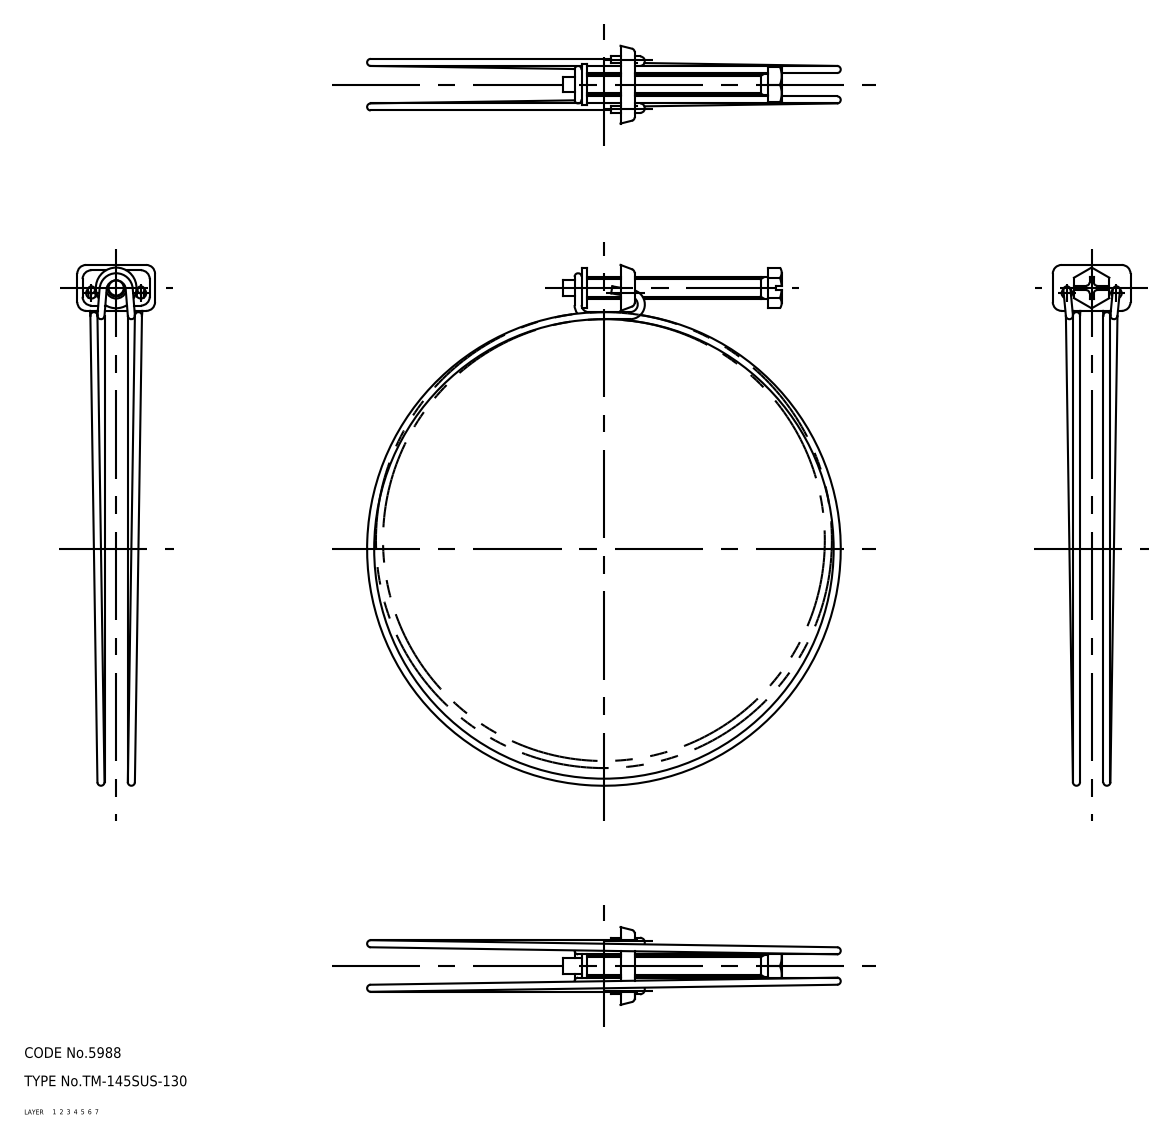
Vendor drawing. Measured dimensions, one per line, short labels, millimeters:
name: screw; holder; band; TM_145SUS_130_21435_36
written by: CADfix (AUTOMOTIVE_DESIGN)
unit: mm
bodies: 3 solids, 119 faces (0 planar, 0 cylindrical, 119 other)
size: 147.35 × 134 × 22
volume: 5 366 mm³; area: 8 141 mm²
